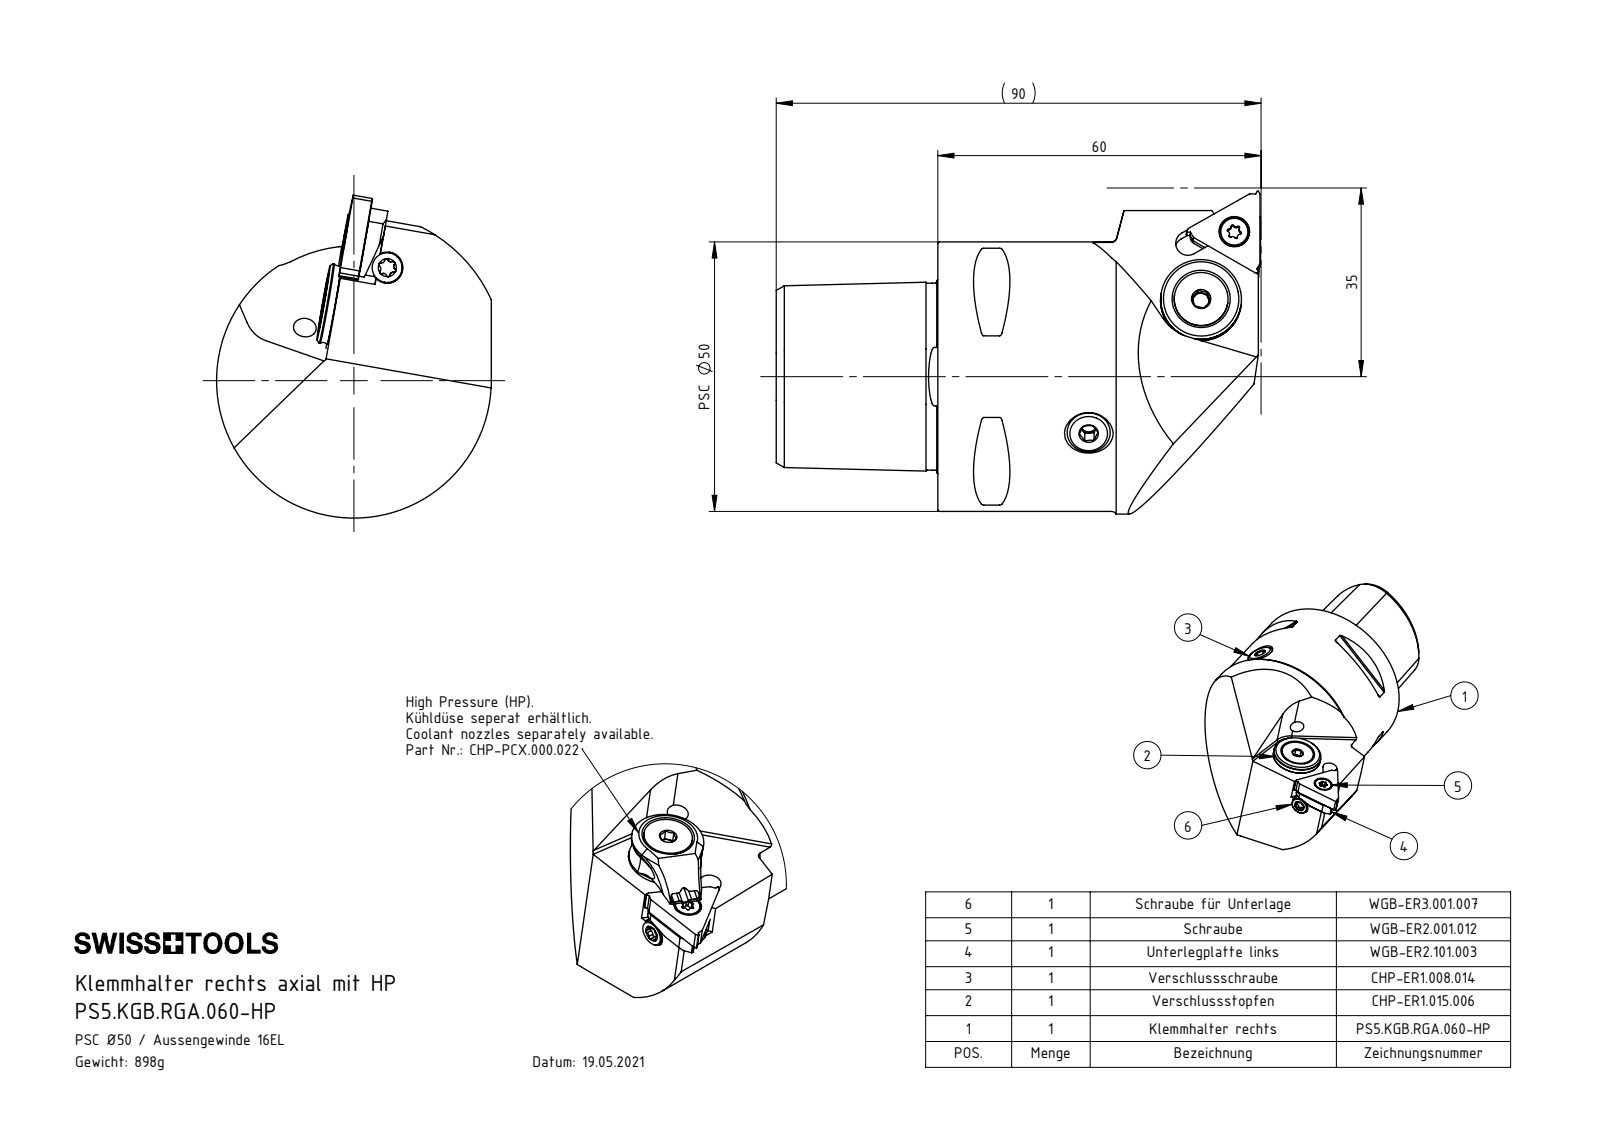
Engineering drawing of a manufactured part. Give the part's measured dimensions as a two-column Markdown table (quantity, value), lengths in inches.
| quantity | value |
| --- | --- |
| part name | CHP-ER1.015.006; LT16EL; DIN 3771 - 13x1; WGB-ER3.001.007_A (+8 more) |
| STEP written by | SolidWorks 2017 (AUTOMOTIVE_DESIGN) |
| units | inches |
| bodies | 10 solids, 313 faces (126 planar, 85 cylindrical, 102 other) |
| overall size | 3.54 × 2.359 × 2.008 |
| volume | 6.98 in³ |
| surface area | 36.68 in² |
| round holes (diameter × count) | 0.165 × 4, 0.102 × 2, 0.157 × 2, 0.047 × 1, 0.079 × 1, 0.098 × 1, 0.118 × 1, 0.158 × 1, 0.205 × 1, 0.24 × 1, 0.276 × 1, 0.571 × 1 |
| round bosses / shafts (diameter × count) | 0.217 × 3, 1.969 × 1, 0.591 × 1, 0.528 × 1, 0.394 × 1, 0.315 × 1, 0.197 × 1, 0.125 × 1 |
| partial cylindrical surfaces (radius × count) | 0.02 × 10, 0.009 × 6, 0.013 × 6, 0.022 × 6, 0.022 × 6, 0.004 × 2, 0.01 × 2, 0.051 × 1 |
| main face-to-face distances | 1.181, 0.177, 0.755, 1.748, 0.144, 0.394, 0.787, 0.046, 0.131, 0.189 |
| hole center spacings | 0.178, 0.437, 0.438, 0.567, 0.568, 0.177, 0.179, 0.437 |
